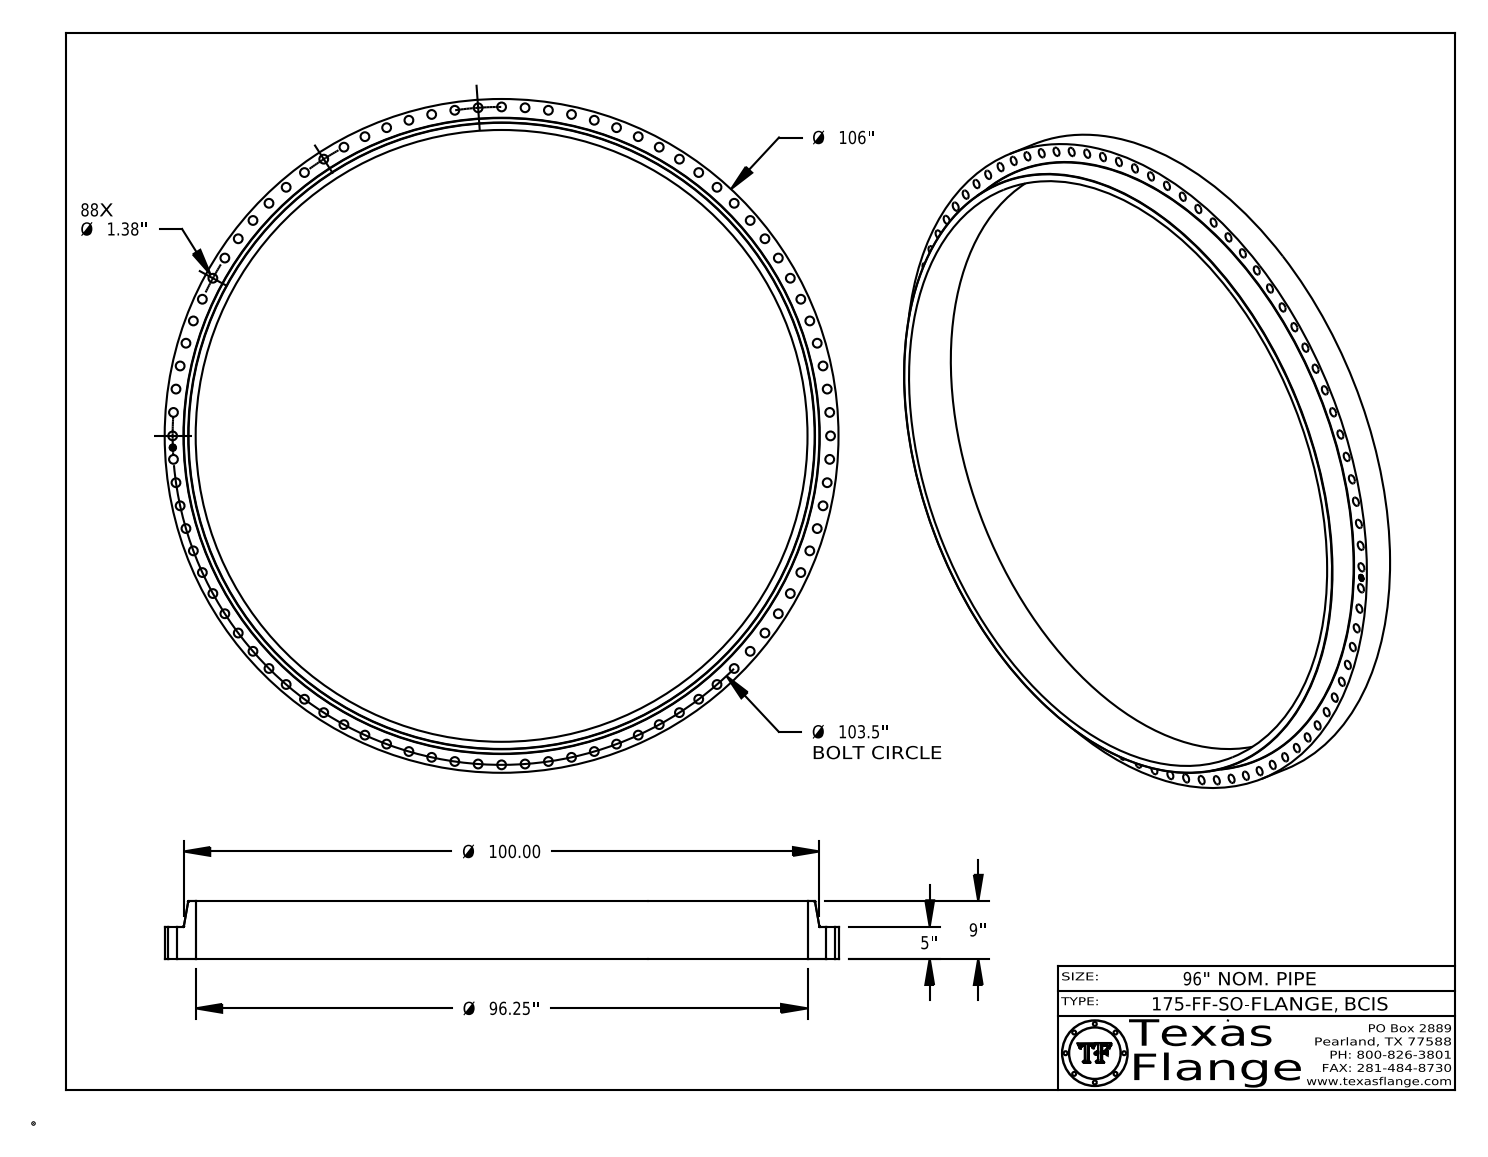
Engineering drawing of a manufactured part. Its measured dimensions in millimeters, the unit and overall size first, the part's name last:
Units: millimetres
Overall size (bounding box): 2692.4 × 2692.4 × 228.6
Round holes (diameter × count): ⌀35.1 ×88, ⌀25.4 ×1, ⌀2444.8 ×1
Round bosses / shafts (diameter × count): ⌀1.5 ×8, ⌀2692.4 ×1, ⌀20 ×1
Main face-to-face distances: 127, 228.6, 101.6, 0.4, 126.6, 102, 7.6, 7.4, 1.4, 4.9
Hole centre spacings: 1314.5, 93.8, 2622.2, 2613.8, 187.5, 2602.2, 2627.2, 281
Volume: 146 800 000 mm³ · Surface area: 6 558 000 mm²
Bodies: 1 solid, 574 faces (368 planar, 200 cylindrical, 6 other)
Part name (STEP PRODUCT): BCIS, Class 175-FF-SO
STEP written by: CATIA V5 STEP AP214 (AUTOMOTIVE_DESIGN)
